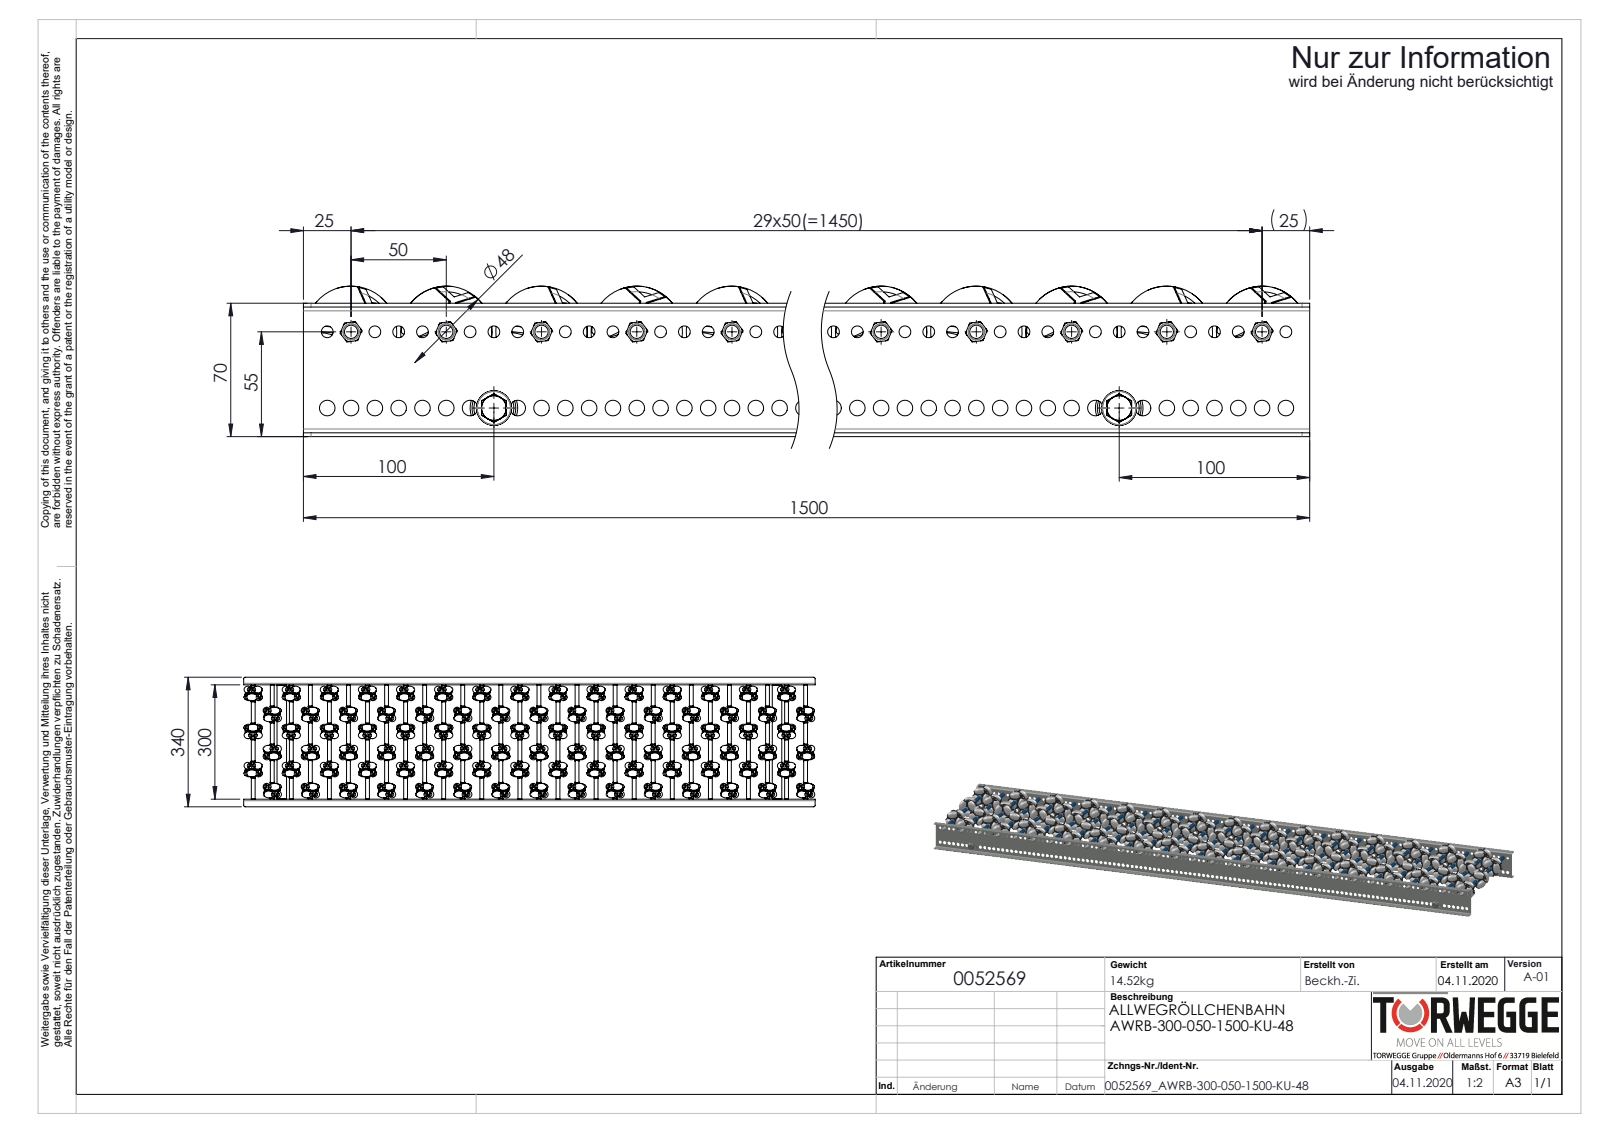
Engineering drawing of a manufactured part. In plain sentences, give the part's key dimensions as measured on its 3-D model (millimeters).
The part is named "0015028_AWR48; AWR48_Halter; AWR48_Stift; AWR-Achse-für-Konfiguration_L300 (+8 more)". Its 3-D file was written by "SolidWorks 2020 (AUTOMOTIVE_DESIGN)". It is 1542 solids with 27692 faces: 9480 planar, 10668 cylindrical and 7544 other. Overall it measures 1500 by 340 by 79 millimeters. Its volume is 5 044 000 cubic millimeters and its surface area 3 458 000 square millimeters. Round holes: 540 of diameter 3.7, 540 of diameter 4.2, 119 of diameter 6.2, 119 of diameter 8.2, 30 of diameter 4.92, 30 of diameter 6.5, 30 of diameter 8.4, 2 of diameter 6.8, 2 of diameter 21. Round bosses or shafts: 540 of diameter 4, 484 of diameter 3.7, 32 of diameter 8, 30 of diameter 42, 30 of diameter 11, 30 of diameter 10, 30 of diameter 7, 30 of diameter 6. Partial cylindrical surfaces (rounded edges, fillets, slot ends): 30 of radius 23.55, 8 of radius 4, 4 of radius 2. The main face-to-face distances are 2, 302, 68, 300, 304, 70, 66, 5, 20, 99.8. The hole center spacings are 36.06, 36.05, 36.07, 4, 169.07, 8, 22.11, 40.92.
